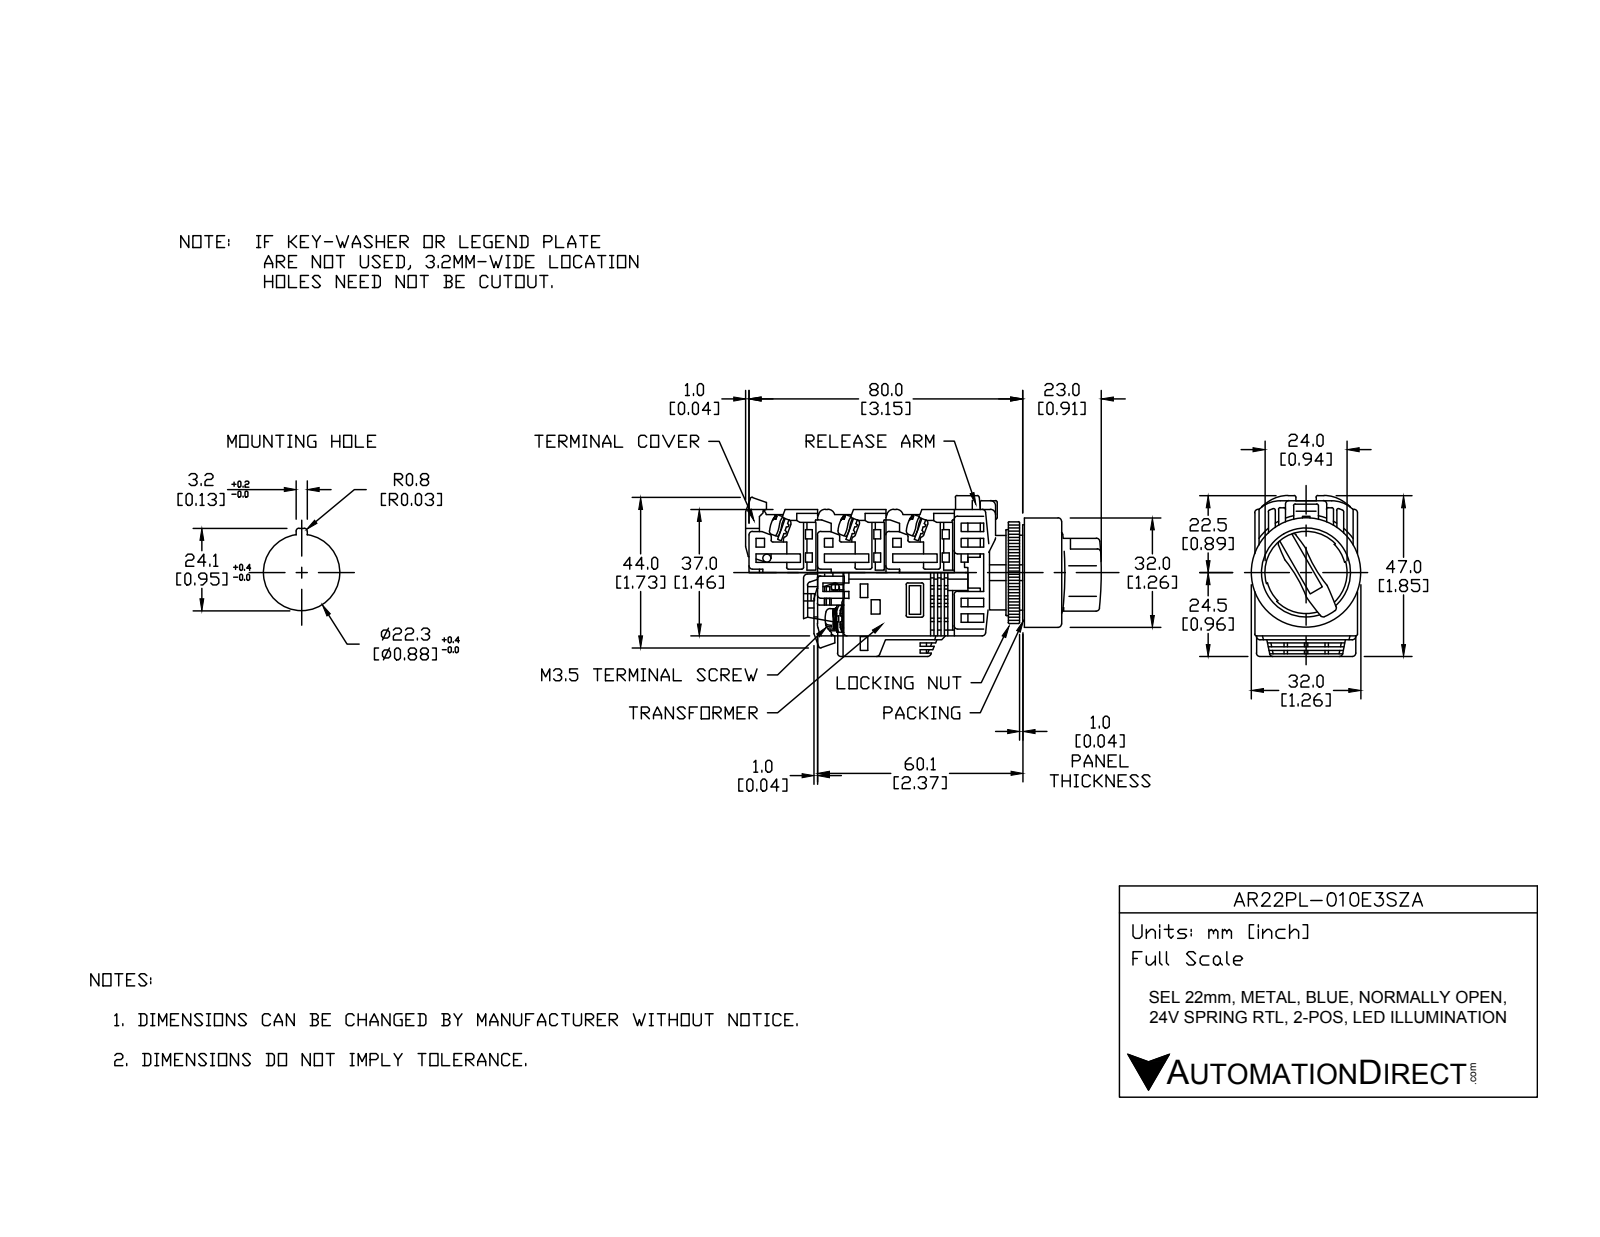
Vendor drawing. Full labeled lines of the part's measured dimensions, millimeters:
Part name (STEP PRODUCT): AR22PL-010E3SZA
STEP written by: SolidWorks 2017 (AUTOMOTIVE_DESIGN)
Units: millimetres
Bodies: 18 solids, 462 faces (317 planar, 118 cylindrical, 27 other)
Overall size (bounding box): 64.5 × 43.81 × 32
Volume: 38 531 mm³ · Surface area: 24 831 mm²
Round holes (diameter × count): ⌀21.8 ×1, ⌀22 ×1, ⌀25 ×1, ⌀31 ×1
Round bosses / shafts (diameter × count): ⌀5 ×4, ⌀32 ×1, ⌀30.5 ×1, ⌀29.8 ×1, ⌀24 ×1, ⌀21.75 ×1, ⌀17 ×1
Partial cylindrical surfaces — rounded edges, fillets, slot ends (radius × count): R0.5 ×39, R1.75 ×8, R1 ×6, R5 ×4, R4 ×2, R12 ×1, R16.59 ×1, R17.59 ×1
Main face-to-face distances: 1, 18, 3, 28.5, 48.5, 20, 29, 0.5, 2, 31
